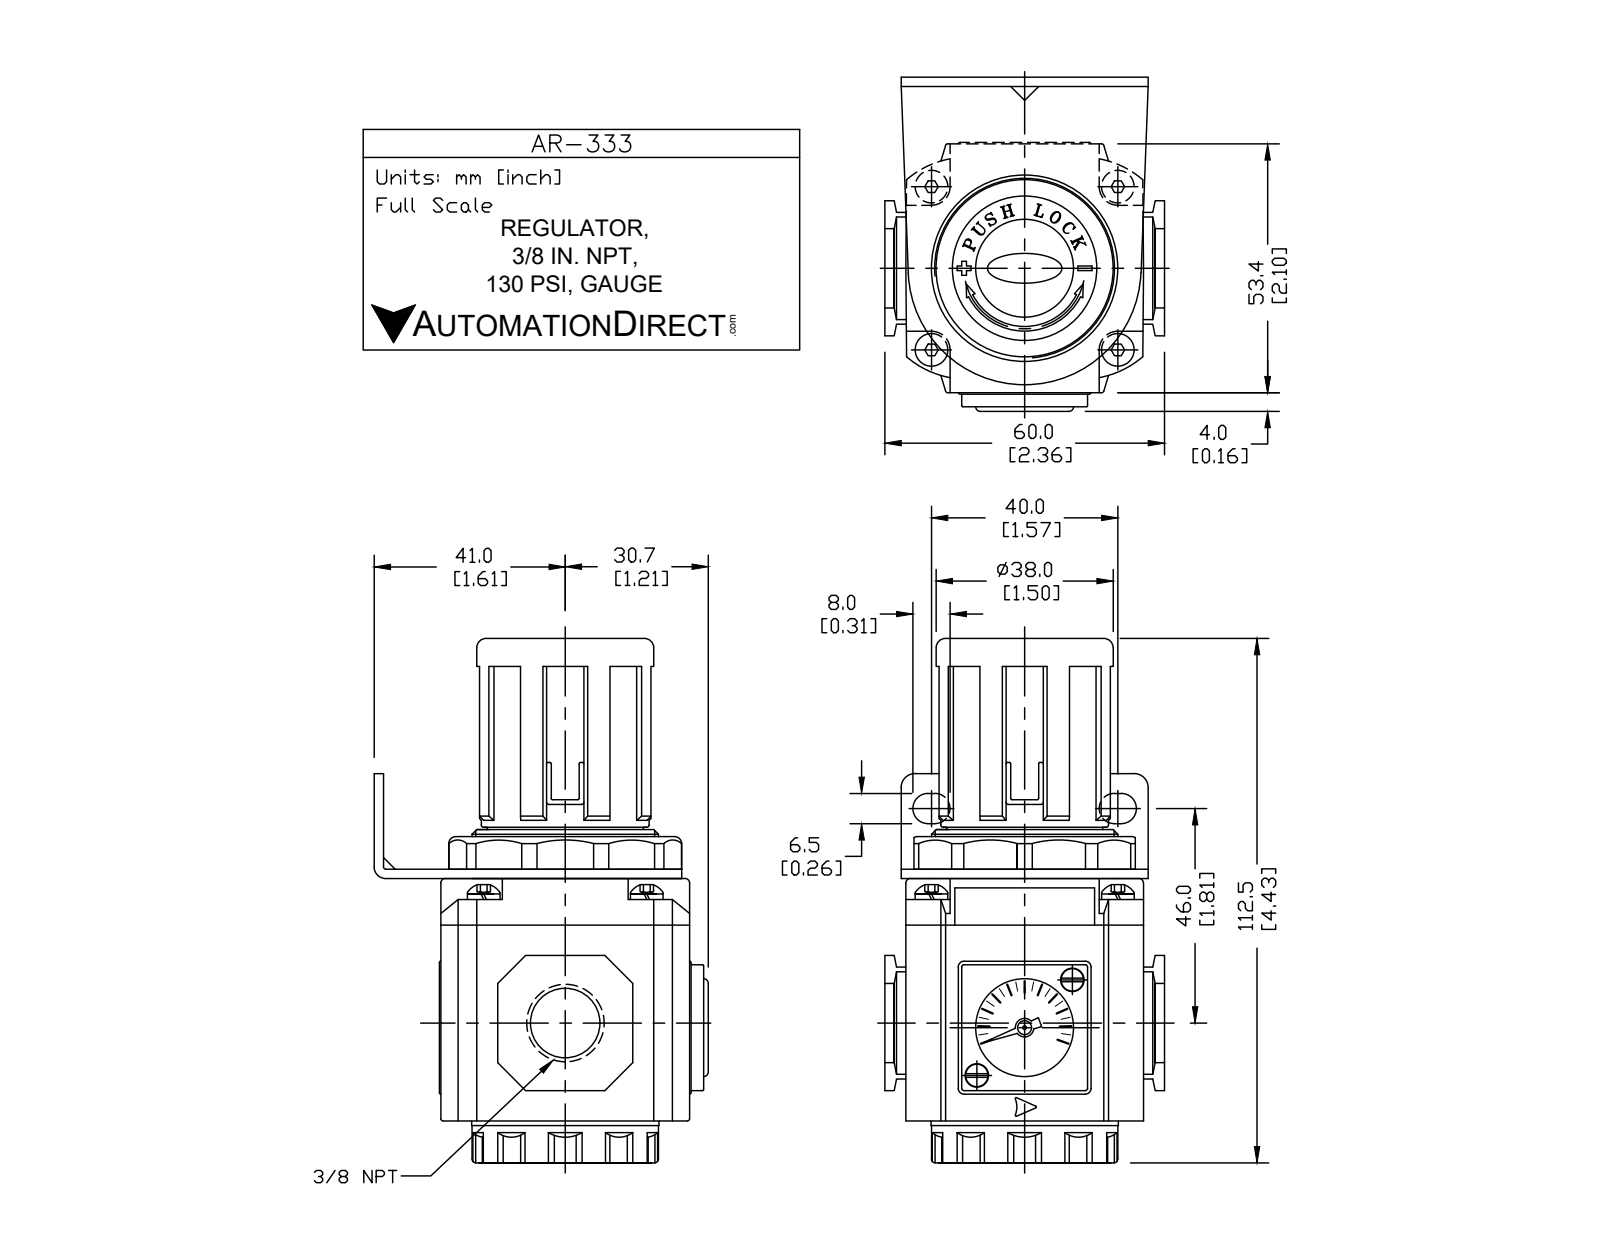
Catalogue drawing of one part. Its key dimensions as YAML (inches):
part_name: "AR-333"
step_written_by: "SolidWorks 2015 (CONFIG_CONTROL_DESIGN)"
units: inches
bodies: {solids: 14, faces: 501, planar: 326, cylindrical: 133, other: 42}
overall_size: [4.429, 2.783, 2.362]
volume: 12.67
surface_area: 68.21
round_holes:
  - {diameter: 0.118, count: 6}
  - {diameter: 0.079, count: 1}
  - {diameter: 0.562, count: 1}
  - {diameter: 0.827, count: 1}
  - {diameter: 1.181, count: 1}
  - {diameter: 1.26, count: 1}
round_bosses_or_shafts:
  - {diameter: 0.217, count: 4}
  - {diameter: 0.106, count: 2}
  - {diameter: 1.575, count: 1}
  - {diameter: 1.543, count: 1}
  - {diameter: 1.496, count: 1}
  - {diameter: 1.319, count: 1}
  - {diameter: 0.806, count: 1}
  - {diameter: 0.157, count: 1}
partial_cylinders:
  - {radius: 0.039, count: 12}
  - {radius: 0.047, count: 10}
  - {radius: 0.128, count: 6}
  - {radius: 0.157, count: 5}
  - {radius: 0.012, count: 4}
  - {radius: 0.783, count: 4}
  - {radius: 0.008, count: 3}
  - {radius: 0.079, count: 1}
face_to_face_distances: [0.079, 2.047, 2.126, 2.102, 0.039, 0.354, 2.402, 2.008, 2.185, 2.063]
hole_center_spacings: [1.046, 0.571, 1.378, 1.575, 2.093, 1.141]
